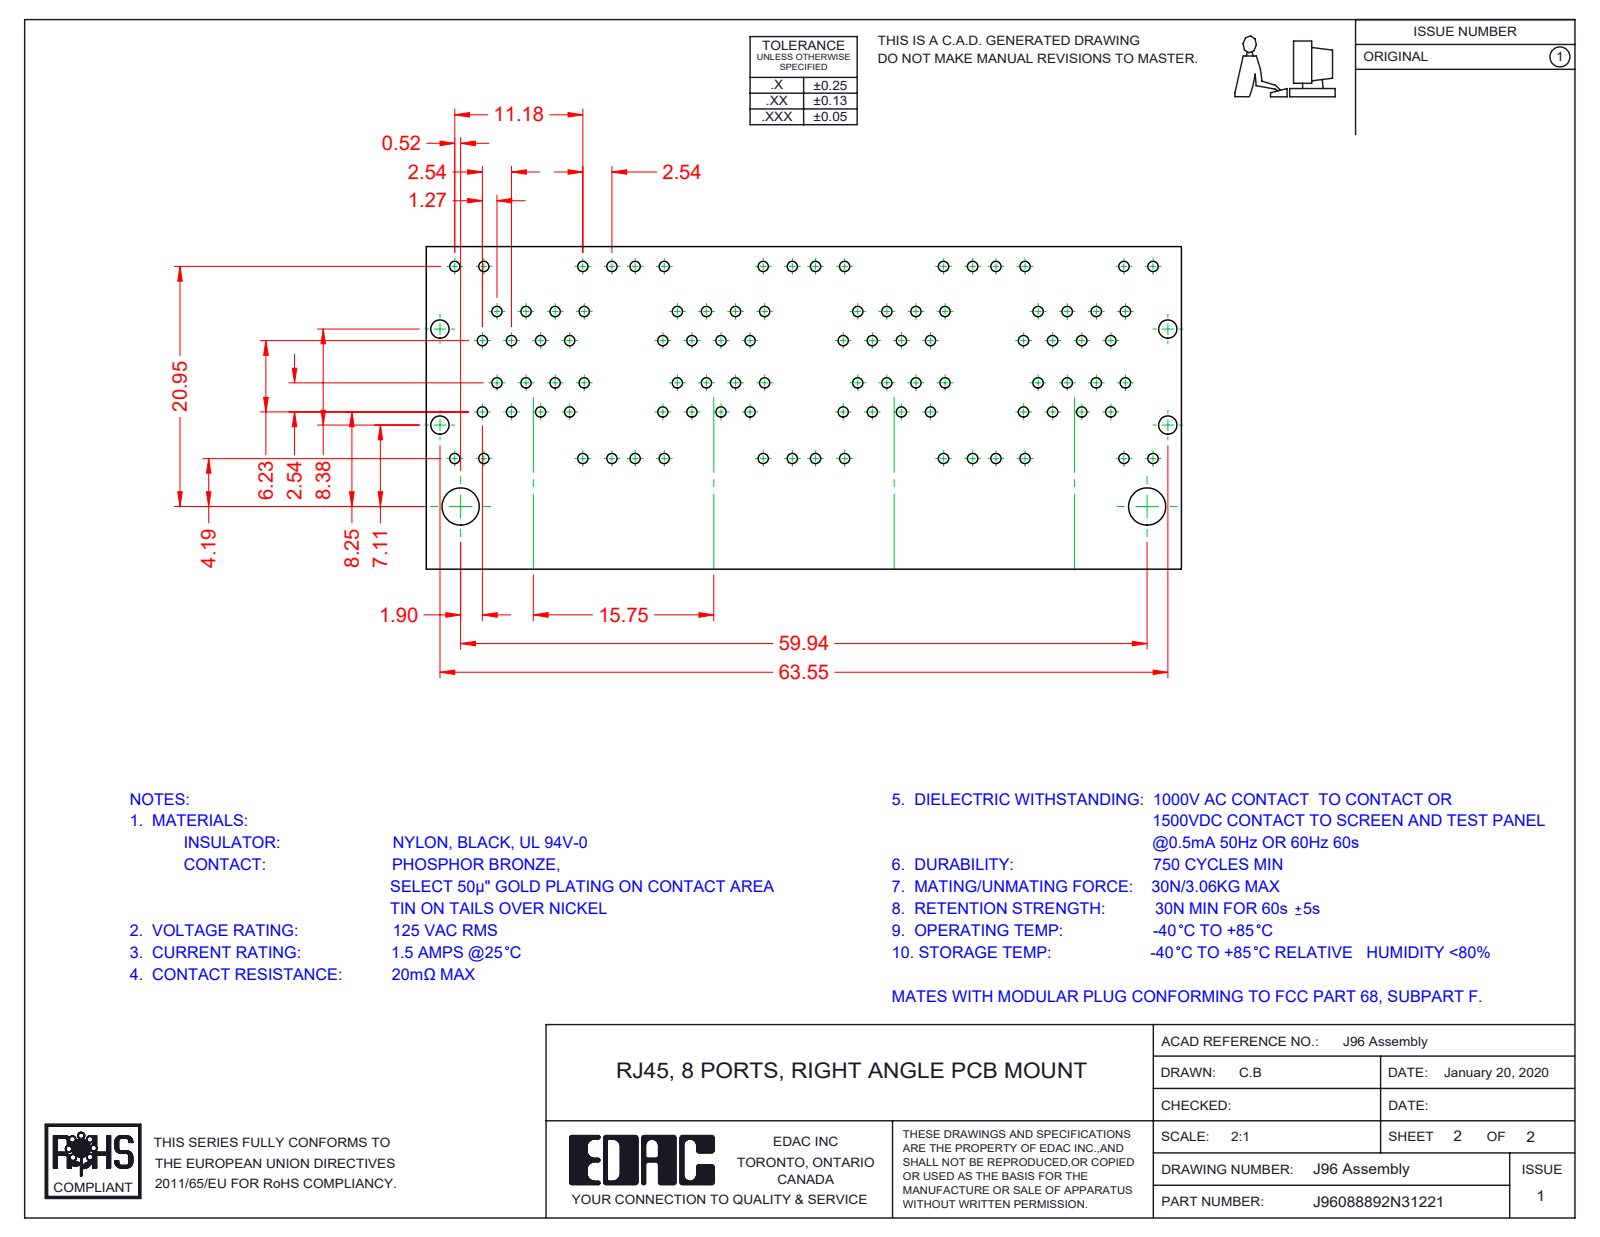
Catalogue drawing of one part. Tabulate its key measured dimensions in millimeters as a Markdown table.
| quantity | value |
| --- | --- |
| part name | 96 LED LH Lower_3-Green; 96 LED RH Upper_1-Yellow; 96 Insulator_8 Ports; 96 Contacts Upper (+8 more) |
| STEP written by | SolidWorks 2016 (CONFIG_CONTROL_DESIGN) |
| units | millimeters |
| bodies | 96 solids, 7804 faces (6105 planar, 1388 cylindrical, 311 other) |
| overall size | 67.35 × 31.38 × 28.68 |
| volume | 24 149 mm³ |
| surface area | 63 596 mm² |
| round holes (diameter × count) | 1.7 × 3 |
| round bosses / shafts (diameter × count) | 1.68 × 3 |
| partial cylindrical surfaces (radius × count) | 0.25 × 124, 0.35 × 73, 1 × 72, 0.5 × 49, 0.91 × 32, 0.2 × 27, 0.27 × 14, 0.7 × 11 |
| main face-to-face distances | 15.75, 0.35, 9.95, 1.17, 1.6, 0.54, 9.98, 10.18, 12.67, 3.37 |
| hole center spacings | 15.75, 31.5 |
